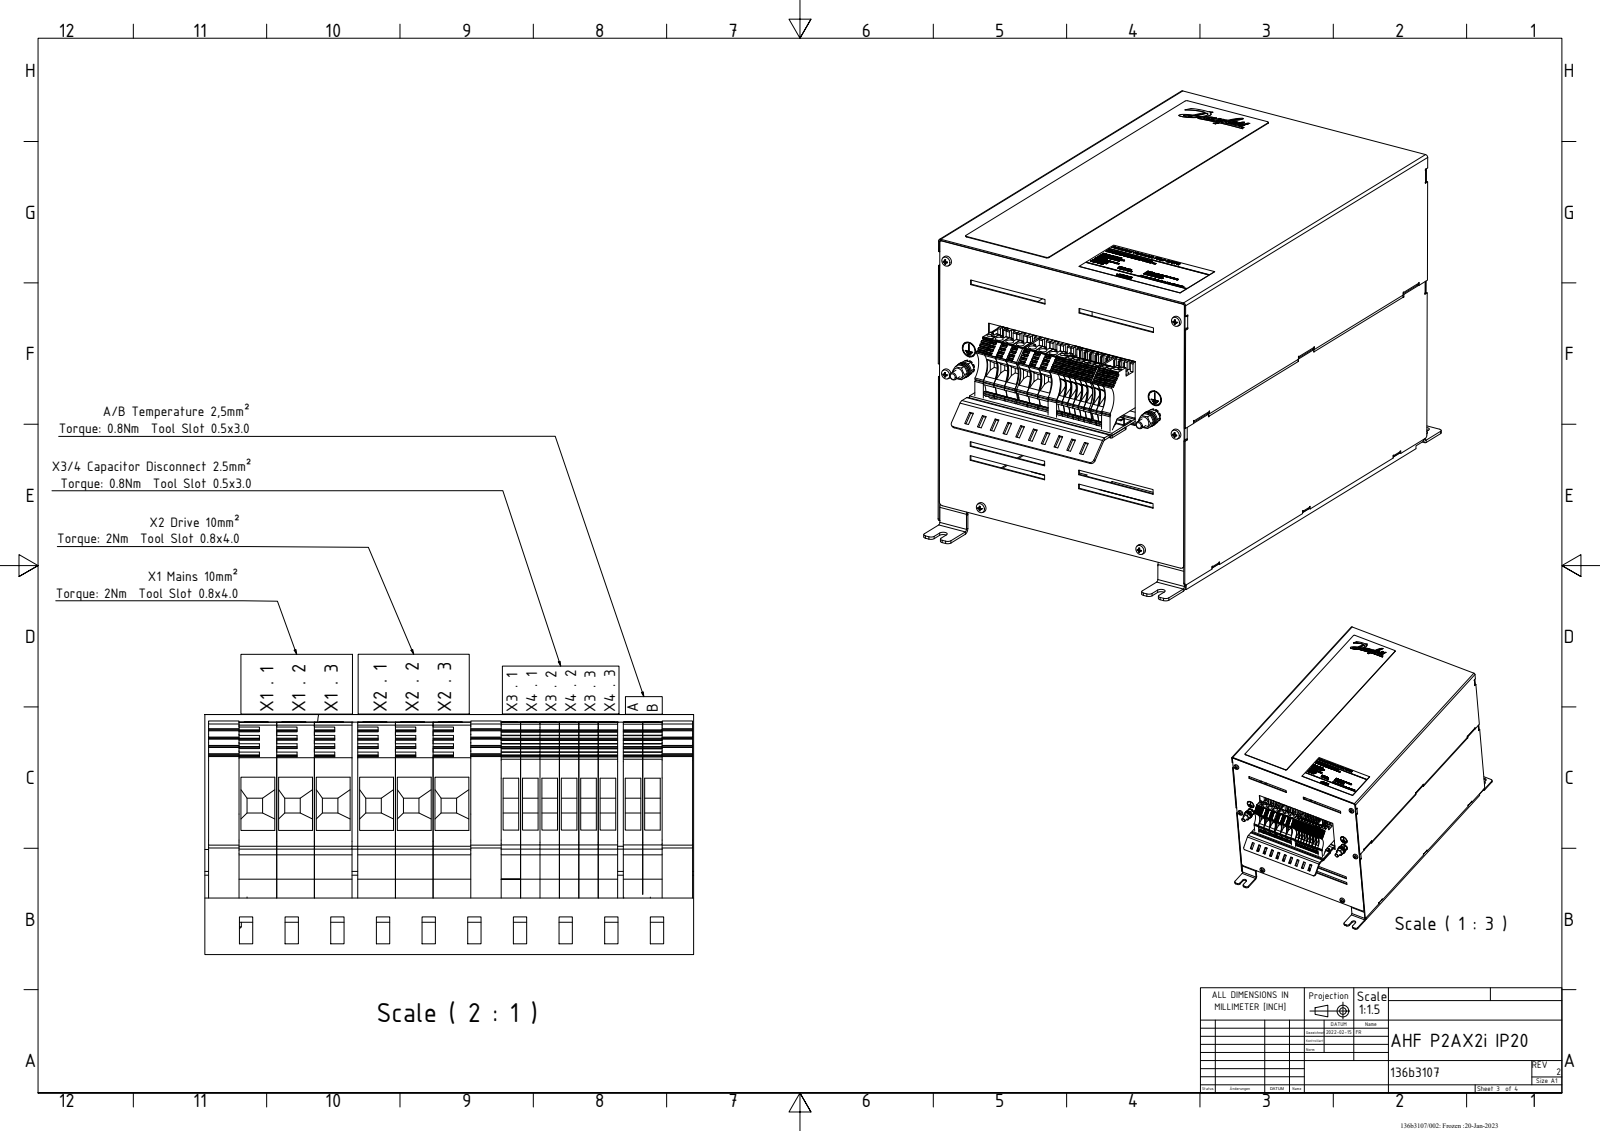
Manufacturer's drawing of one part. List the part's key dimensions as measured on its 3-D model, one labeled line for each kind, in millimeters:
Part name (STEP PRODUCT): X2
STEP written by: CREO PARAMETRIC BY PTC INC, 2020342 (CONFIG_CONTROL_DESIGN)
Units: millimetres
Bodies: 3 solids, 2683 faces (2379 planar, 272 cylindrical, 32 other)
Overall size (bounding box): 433.04 × 248.15 × 232.4
Volume: 866 451 mm³ · Surface area: 952 132 mm²
Round holes (diameter × count): ⌀4 ×11, ⌀6.5 ×7, ⌀6.32 ×6, ⌀2 ×4, ⌀12.5 ×4, ⌀34 ×1, ⌀48 ×1, ⌀62 ×1, ⌀76 ×1, ⌀90 ×1, ⌀104 ×1
Round bosses / shafts (diameter × count): ⌀8 ×8, ⌀8.21 ×4, ⌀7.6 ×4, ⌀11.3 ×2, ⌀7.65 ×2, ⌀6 ×2, ⌀107 ×1, ⌀93 ×1
Partial cylindrical surfaces — rounded edges, fillets, slot ends (radius × count): R4.25 ×16, R3.25 ×4, R2 ×3, R1.6 ×1, R2.91 ×1, R3.6 ×1, R3.67 ×1, R3.91 ×1
Main face-to-face distances: 1, 2, 231.2, 231, 1.2, 232.2, 0.8, 231.4, 230.2, 226.5
Hole centre spacings: 5.1, 9.9, 10.2, 74.1, 104.8, 15.3, 31.2, 35
